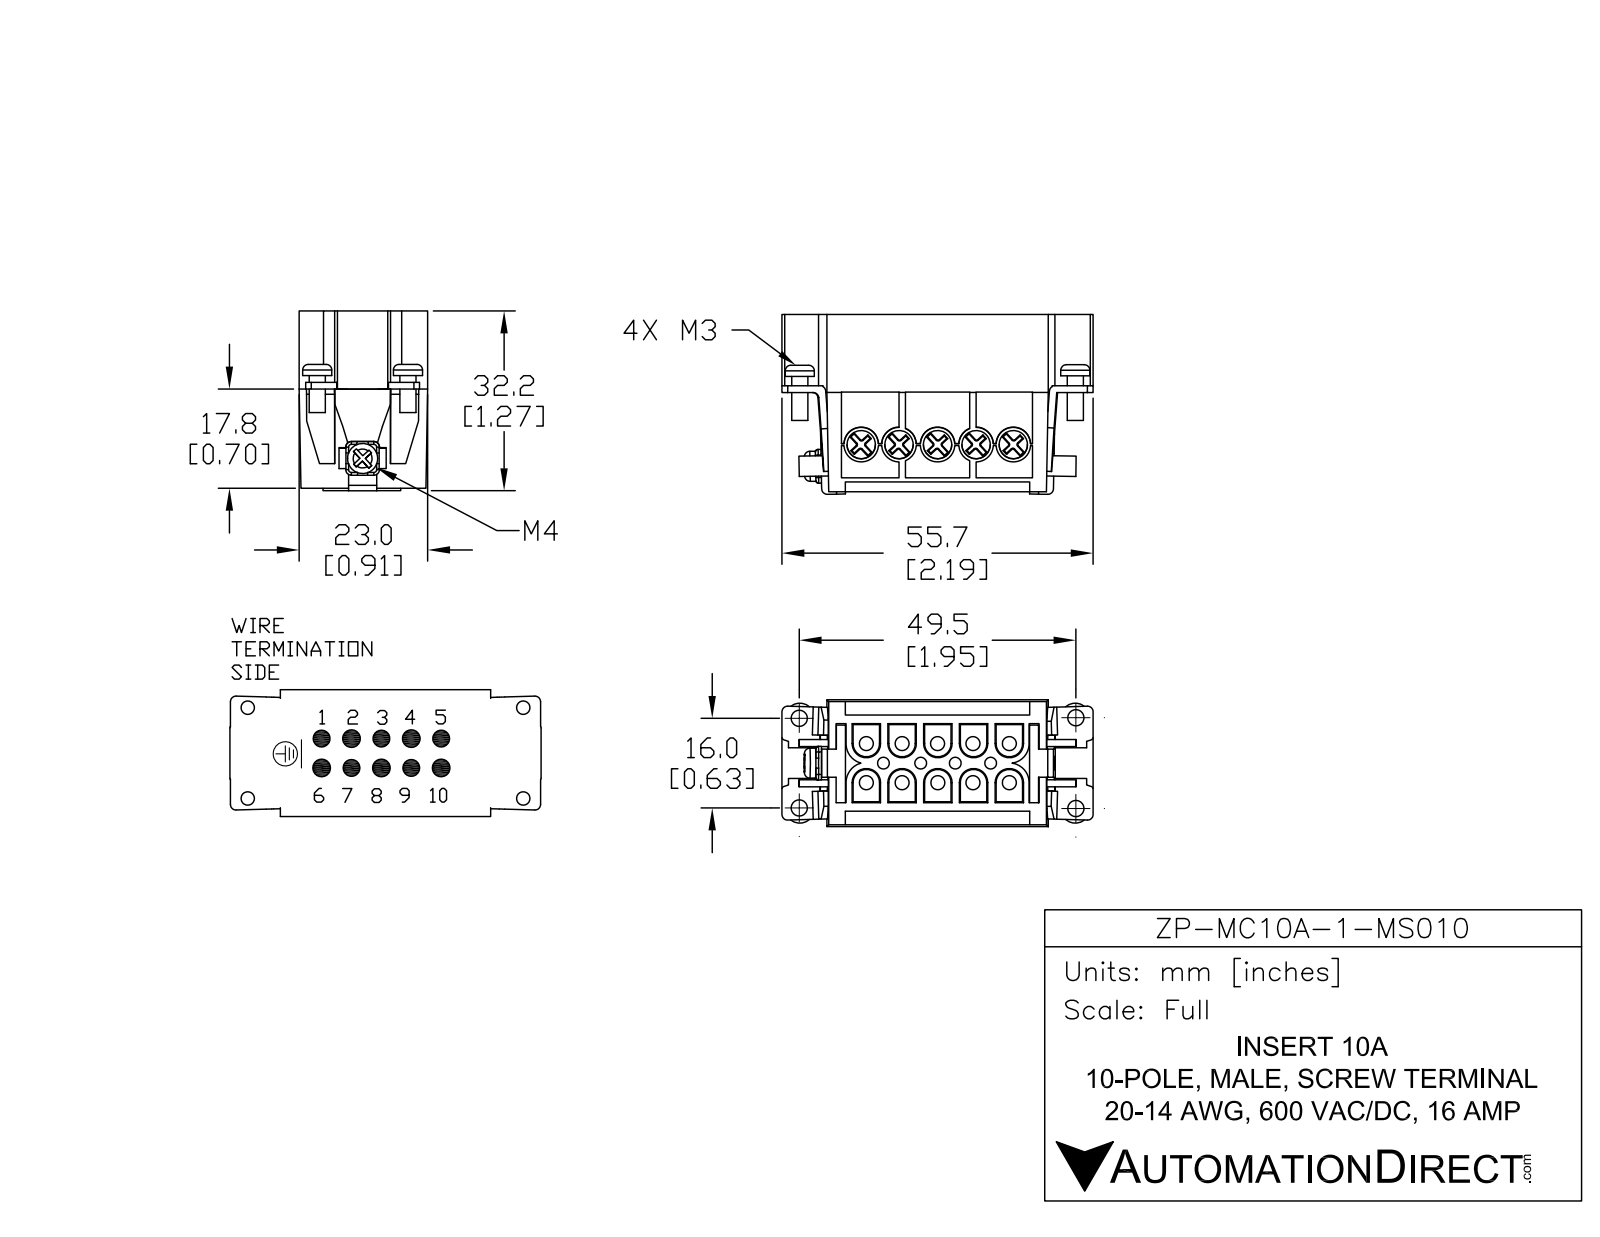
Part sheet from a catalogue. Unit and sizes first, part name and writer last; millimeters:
Units: millimetres
Overall size (bounding box): 55.7 × 32.68 × 22.7
Round holes (diameter × count): ⌀2.5 ×10, ⌀5.06 ×8, ⌀2.1 ×4, ⌀5.06 ×2, ⌀2.49 ×1
Round bosses / shafts (diameter × count): ⌀6.18 ×10, ⌀2.53 ×10, ⌀5.21 ×4, ⌀2.89 ×4, ⌀5.38 ×1
Partial cylindrical surfaces — rounded edges, fillets, slot ends (radius × count): R1 ×20, R0.5 ×12, R3.53 ×2, R3.63 ×2
Main face-to-face distances: 1.44, 21.26, 6.4, 22.7, 15.1, 3, 18.1, 19.82, 12.8, 1.53
Hole centre spacings: 4.72, 7, 4.84, 6.9, 6.4, 9.48, 19.2, 4.65
Volume: 17 389 mm³ · Surface area: 15 290 mm²
Bodies: 1 solid, 781 faces (501 planar, 172 cylindrical, 108 other)
Part name (STEP PRODUCT): ZP-MC10A-1-MS010
STEP written by: SolidWorks 2014 (AUTOMOTIVE_DESIGN)
